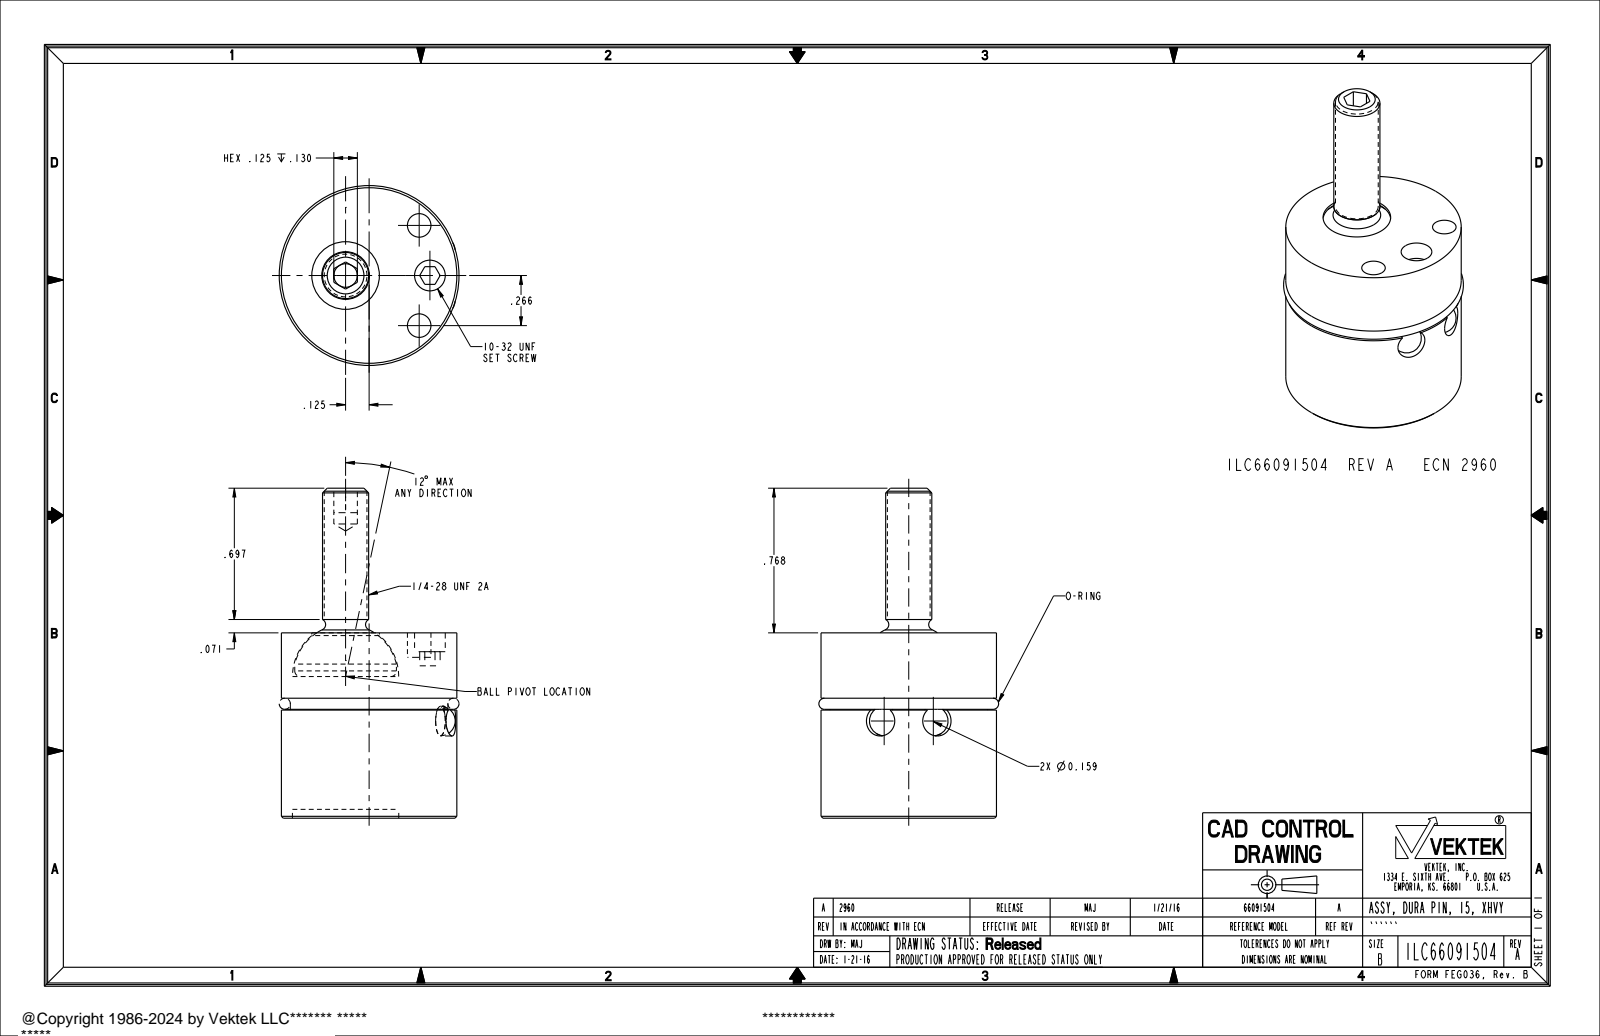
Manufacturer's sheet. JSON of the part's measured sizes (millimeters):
{"part_name": "ILC66091504_BODY; ILC66091504_PIVOT; ILC66091504", "step_written_by": "PRO/ENGINEER BY PARAMETRIC TECHNOLOGY CORPORATION, 2013320 (AUTOMOTIVE_DESIGN)", "units": "millimeters", "bodies": {"solids": 2, "faces": 82, "planar": 34, "cylindrical": 28, "other": 20}, "overall_size": [44.5, 24.3, 24.3], "volume_mm3": 11200, "surface_area_mm2": 4975, "round_holes": [[3.2, 3], [4, 2], [4.1, 1], [9.1, 1], [14.4, 1]], "round_bosses_or_shafts": [[23.7, 1], [21.3, 1], [13.7, 1], [6.2, 1], [5.8, 1]], "face_to_face_distances": [5.9, 19.1, 25, 1.2, 17.9, 23.8, 16.2, 15, 2.9, 8.8], "hole_center_spacings": [6.9, 12, 11.4, 13.5]}
